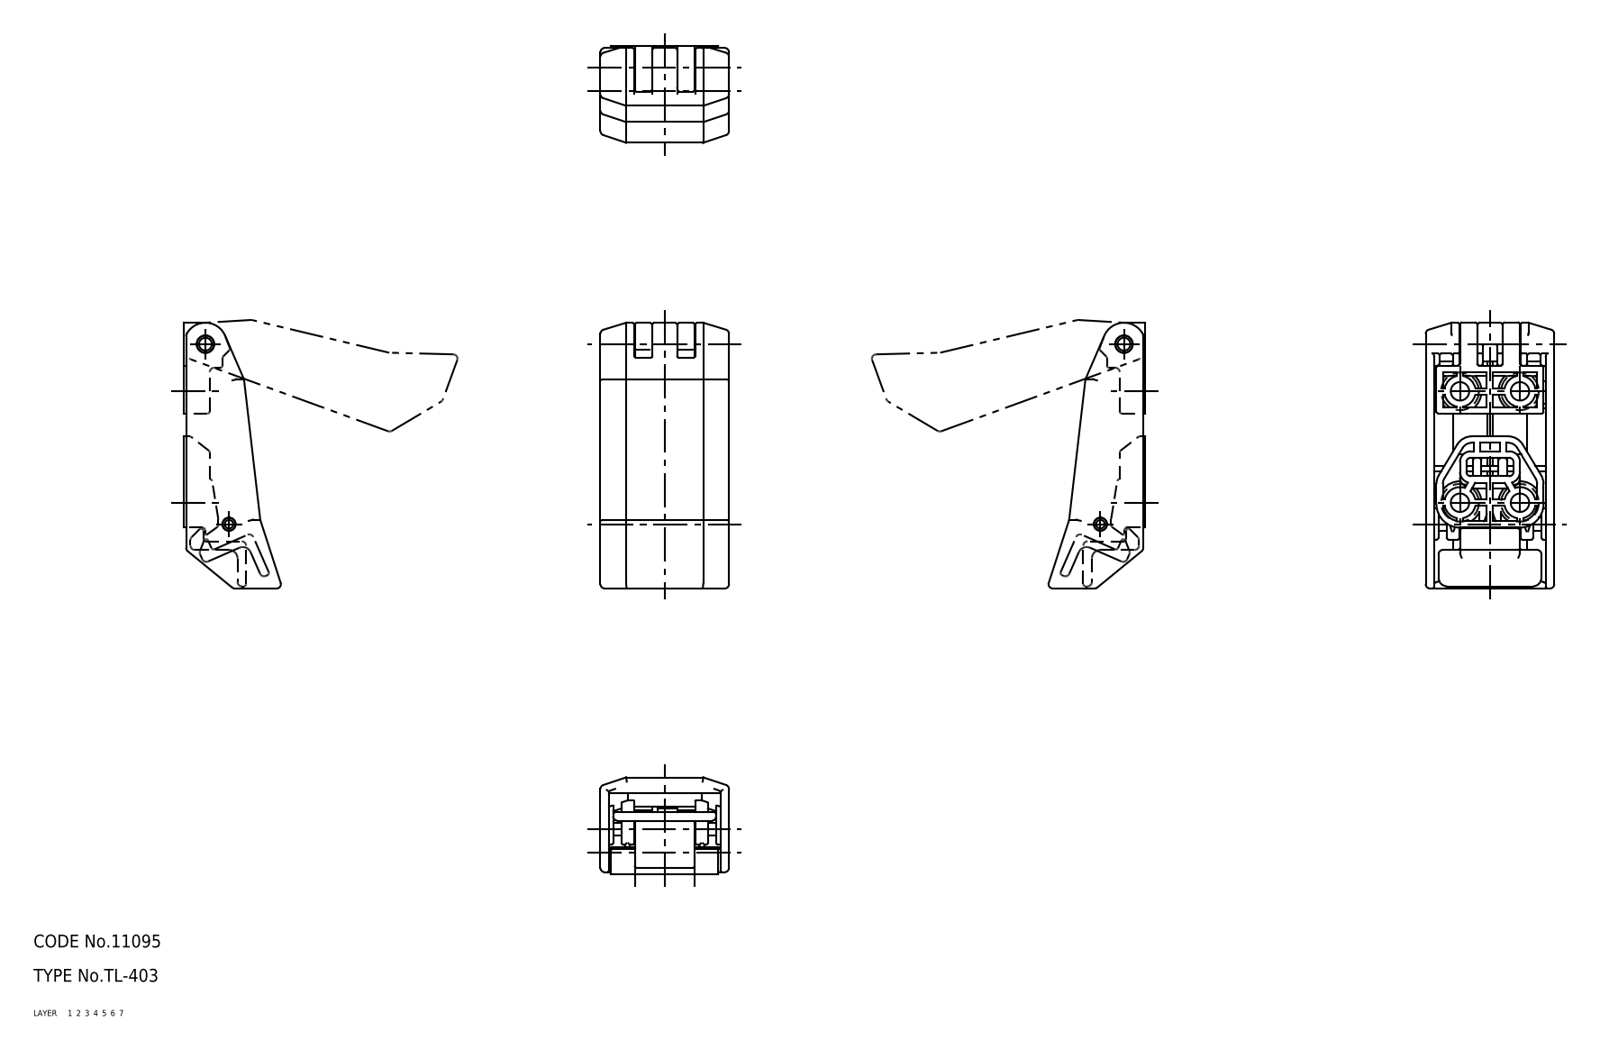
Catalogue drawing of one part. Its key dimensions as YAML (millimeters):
part_name: "cover; base; keeper; TL_403"
step_written_by: "SolidWorks 2015 (AUTOMOTIVE_DESIGN)"
units: millimeters
bodies: {solids: 3, faces: 454, planar: 192, cylindrical: 184, other: 78}
overall_size: [62.1, 30, 22.61]
volume: 14632
surface_area: 13741
round_holes:
  - {diameter: 4.3, count: 4}
  - {diameter: 4, count: 1}
  - {diameter: 4.05, count: 1}
round_bosses_or_shafts:
  - {diameter: 3, count: 1}
partial_cylinders:
  - {radius: 0.5, count: 60}
  - {radius: 1, count: 33}
  - {radius: 4, count: 5}
  - {radius: 2, count: 3}
  - {radius: 1.5, count: 2}
  - {radius: 4.4, count: 2}
  - {radius: 5.5, count: 2}
  - {radius: 0.25, count: 1}
face_to_face_distances: [2, 28, 10, 6, 30, 1.2, 26, 12, 8, 11]
hole_center_spacings: [14, 26, 29.53]
